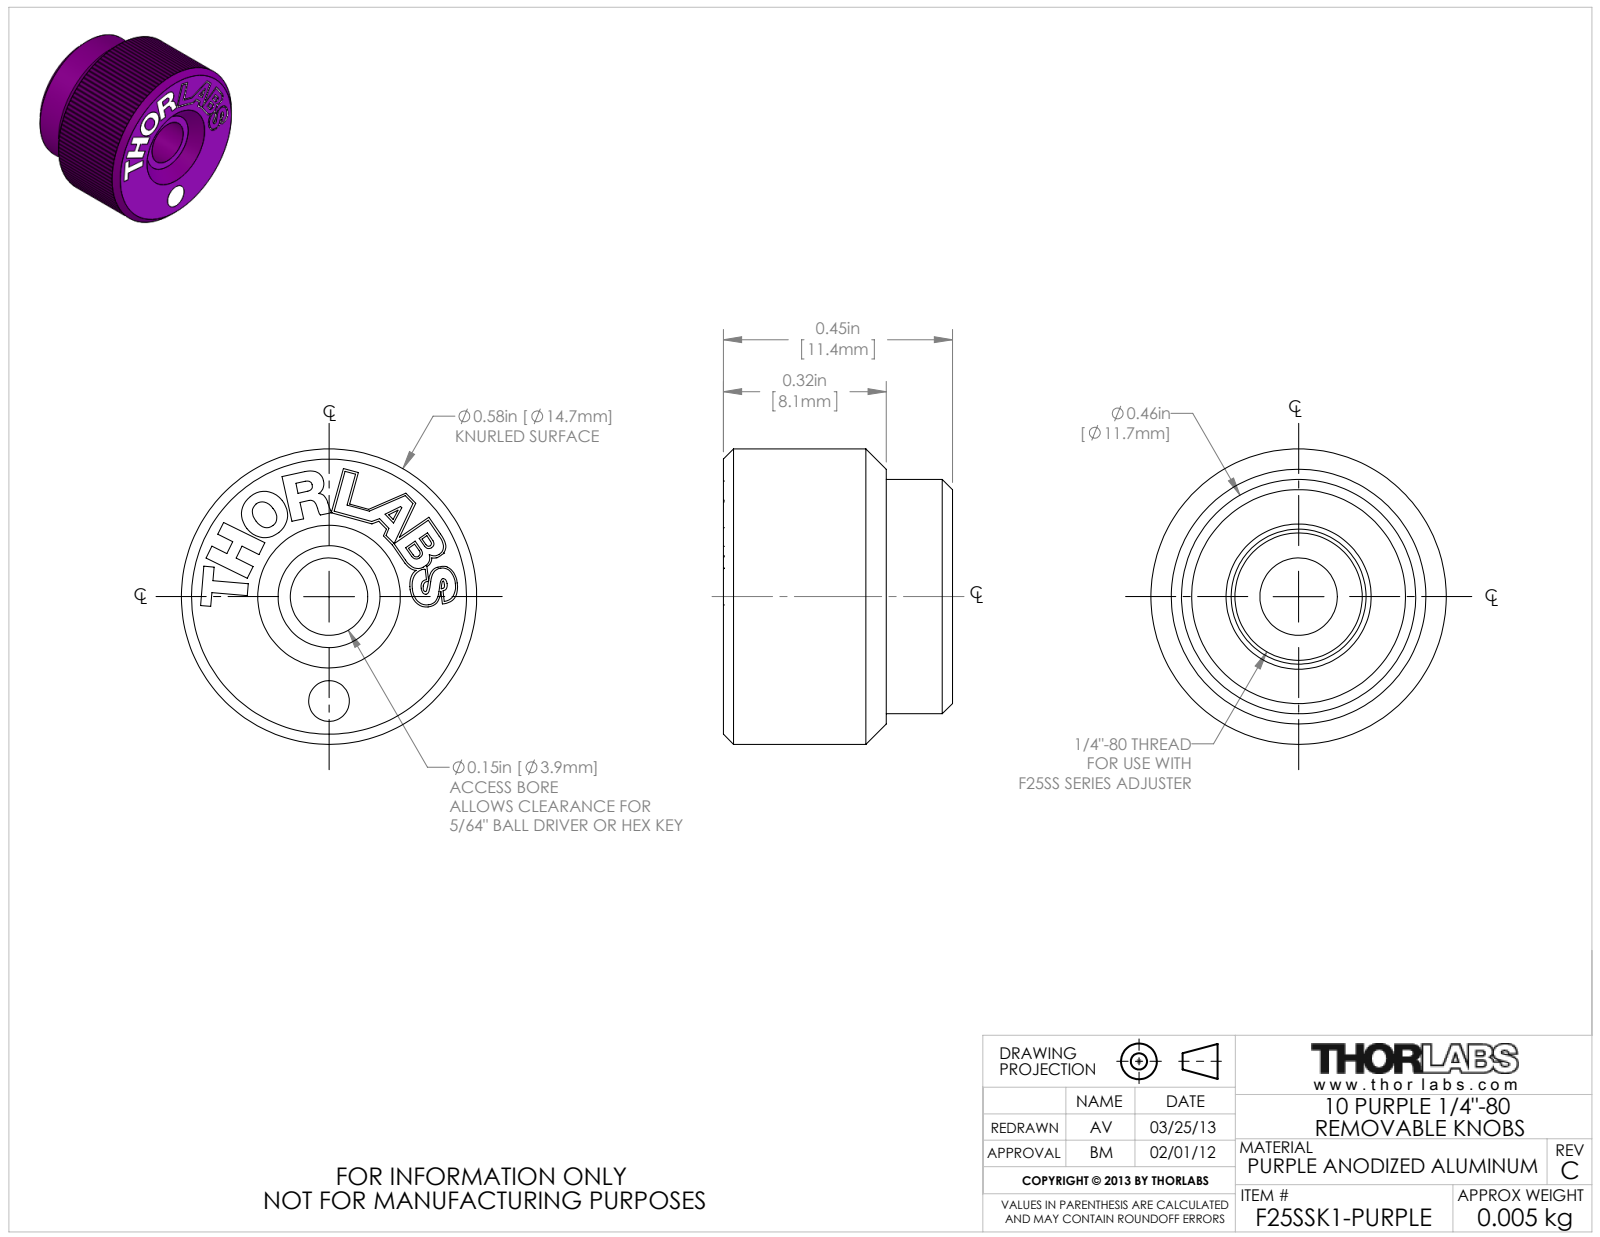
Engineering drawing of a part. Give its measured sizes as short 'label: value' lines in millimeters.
name: 23391-E0W
written by: SolidWorks 2012 (AUTOMOTIVE_DESIGN)
unit: mm
bodies: 1 solid, 210 faces (118 planar, 21 cylindrical, 71 other)
size: 14.7 × 14.7 × 11.4
volume: 1 400 mm³; area: 953 mm²
holes: 1× ⌀2, 1× ⌀3.9, 1× ⌀6.4, 1× ⌀6.7, 1× ⌀7.4
bosses: 1× ⌀14.7, 1× ⌀11.7
rounds: 1× R0.4, 1× R1.2, 1× R1.5
face distances: 11.4, 6.9, 4.6, 8.1, 1.3, 3.3, 6.9, 8.1, 11.4, 0.5
hole spacings: 5.2
